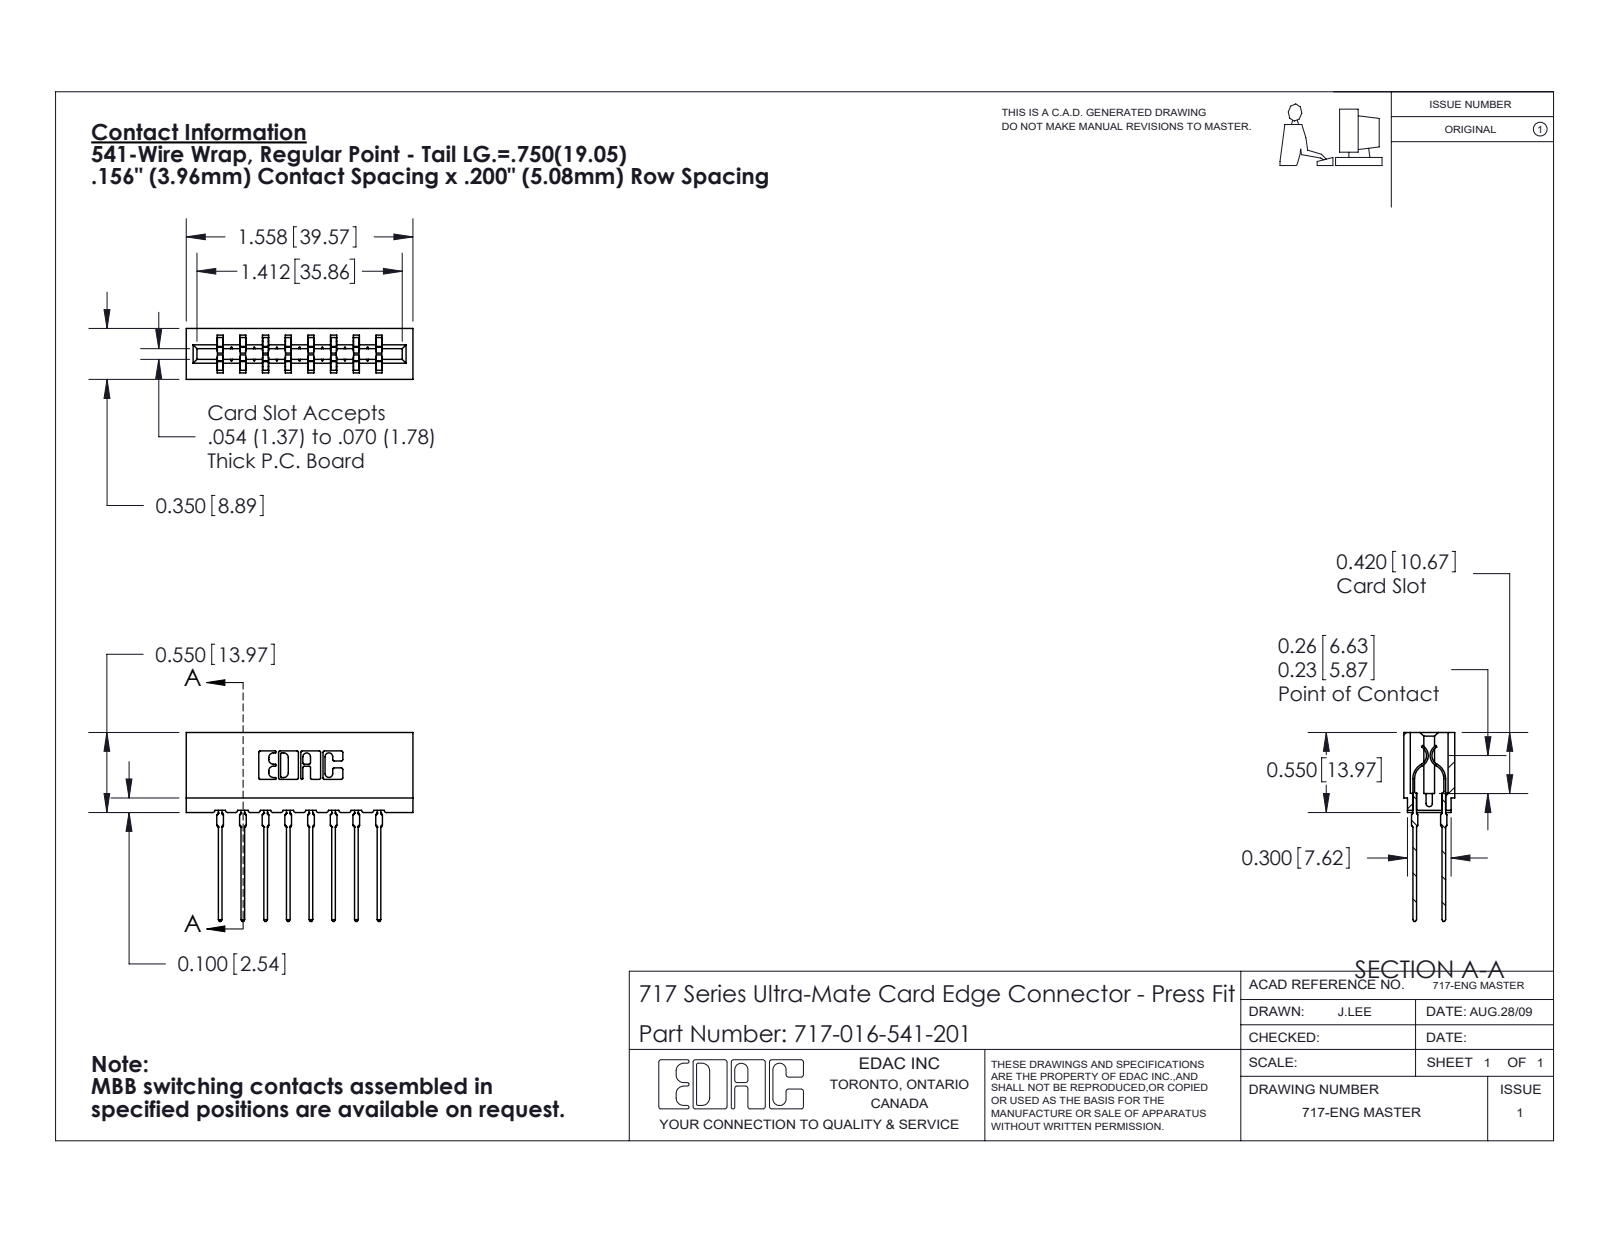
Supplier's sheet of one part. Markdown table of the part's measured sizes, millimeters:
| quantity | value |
| --- | --- |
| part name | 717-016-541-201; 717 Part_Insulator Option - 06; 745-292-001_541 |
| STEP written by | SolidWorks 2020 (CONFIG_CONTROL_DESIGN) |
| units | millimeters |
| bodies | 17 solids, 1534 faces (798 planar, 320 cylindrical, 416 other) |
| overall size | 39.6 × 33 × 8.9 |
| volume | 3 650 mm³ |
| surface area | 5 480 mm² |
| partial cylindrical surfaces (radius × count) | 0.5 × 32, 0.3 × 22, 0.4 × 16, 0.1 × 8, 0.3 × 8, 0.2 × 6, 0.8 × 6, 0.7 × 3 |
| main face-to-face distances | 5.4, 4, 3.5, 15.8, 11.9, 5, 7.9, 8.9, 1.6, 7.3 |
